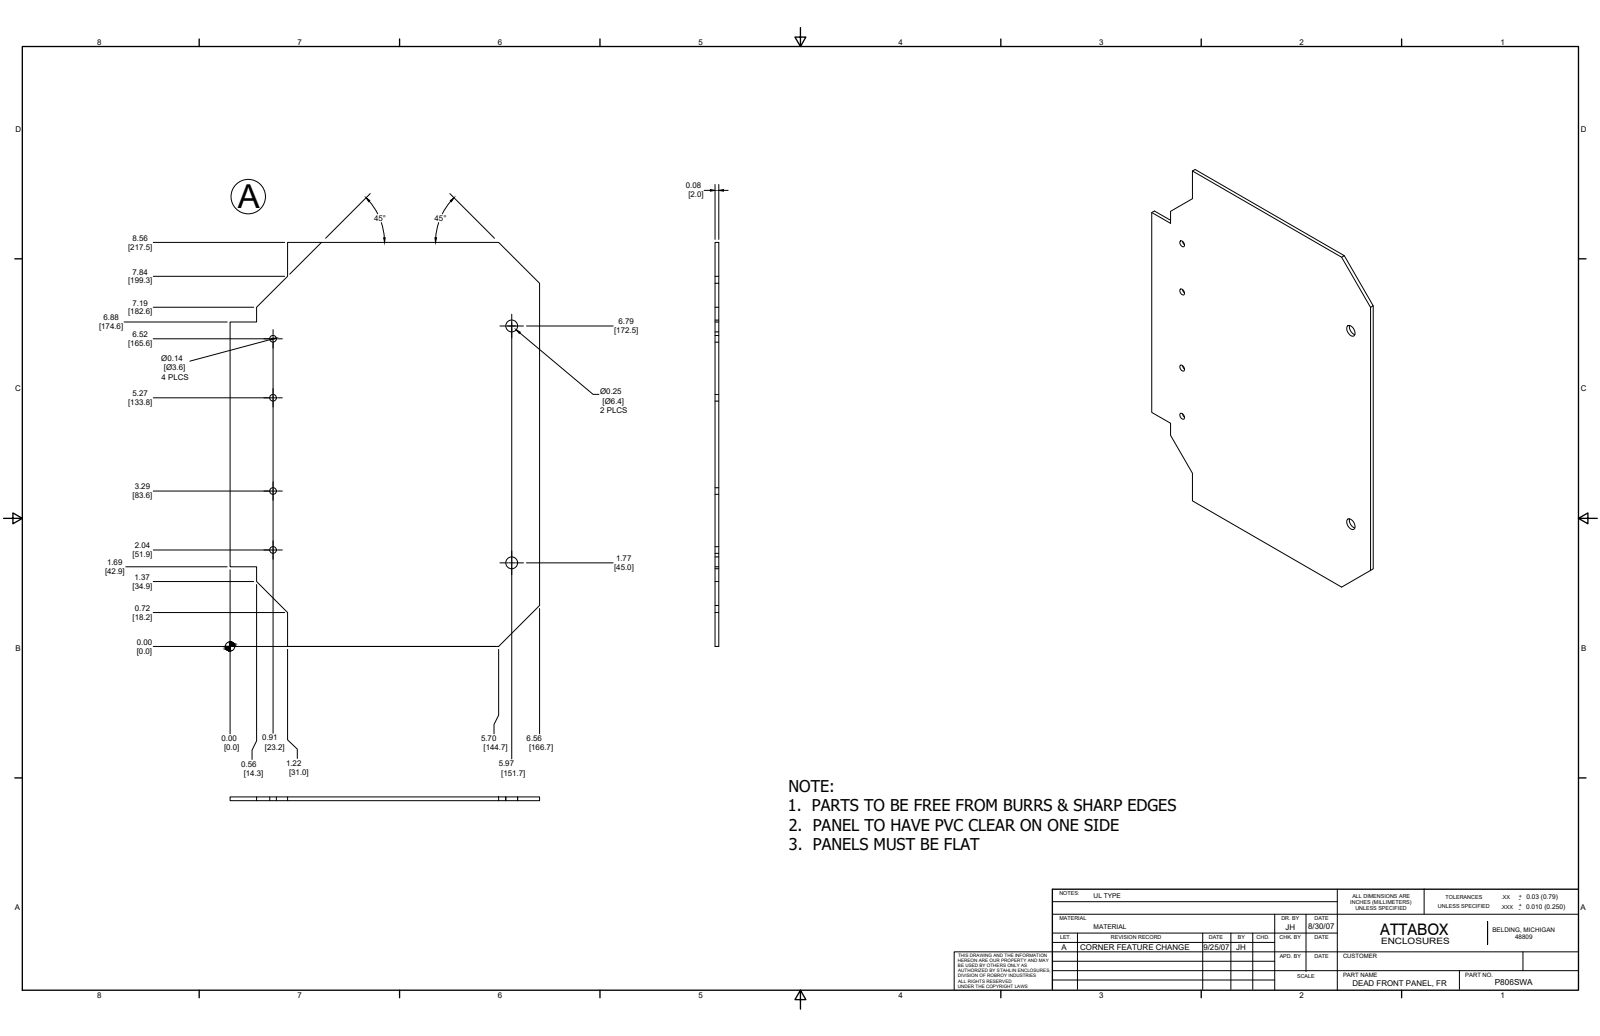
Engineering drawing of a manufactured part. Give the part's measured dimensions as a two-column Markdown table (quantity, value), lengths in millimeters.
| quantity | value |
| --- | --- |
| part name | P806SWAL |
| STEP written by | Autodesk Inventor 11 (AUTOMOTIVE_DESIGN) |
| units | millimeters |
| bodies | 1 solid, 20 faces (14 planar, 6 cylindrical, 0 other) |
| overall size | 217.5 × 166.7 × 2 |
| volume | 69 600 mm³ |
| surface area | 70 130 mm² |
| round holes (diameter × count) | 3.6 × 4, 6.4 × 2 |
| main face-to-face distances | 2, 166.7, 217.5, 27.7, 189.8, 139, 224.6, 162.1 |
| hole center spacings | 31.8, 81.9, 128.7, 134.2, 156.2, 176.2, 50.2, 113.7 |
